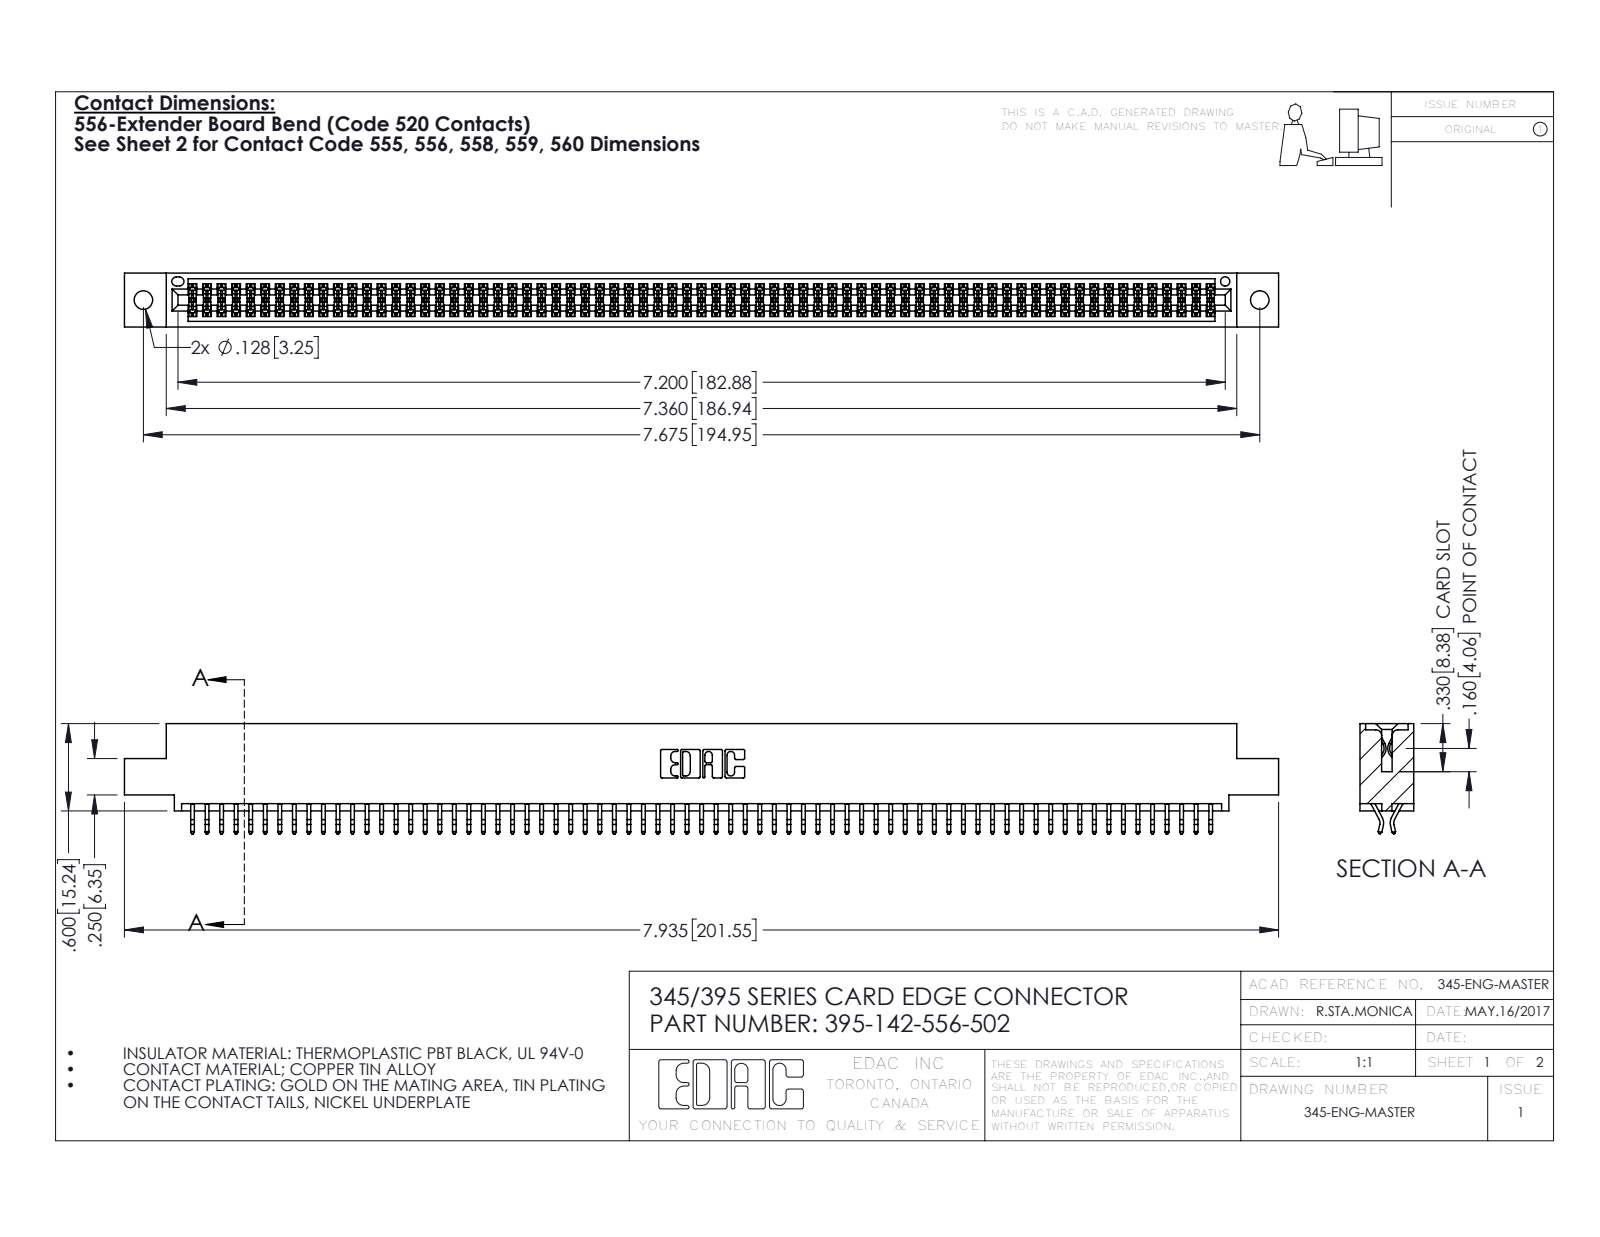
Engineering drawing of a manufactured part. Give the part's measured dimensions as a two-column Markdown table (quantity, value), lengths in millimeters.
| quantity | value |
| --- | --- |
| part name | 345 Part_0.110 Offset - 0.128 Dia; 395-142-556-502; 345-292-001_556 Tail |
| STEP written by | SolidWorks 2016 (CONFIG_CONTROL_DESIGN) |
| units | millimeters |
| bodies | 143 solids, 8082 faces (5338 planar, 2744 cylindrical, 0 other) |
| overall size | 201.5 × 19.2 × 9.4 |
| volume | 19 730 mm³ |
| surface area | 29 430 mm² |
| round holes (diameter × count) | 3.3 × 2, 1.6 × 1 |
| partial cylindrical surfaces (radius × count) | 0.2 × 213, 0.3 × 22, 0.2 × 6, 0.8 × 6, 0.7 × 3, 0.3 × 2, 0.4 × 2, 0.5 × 2 |
| main face-to-face distances | 7.6, 1.8, 9.4, 5.1, 0.6, 2.5, 6.9, 5.7, 4.4, 3.8 |
| hole center spacings | 6.9, 189, 194.9 |
